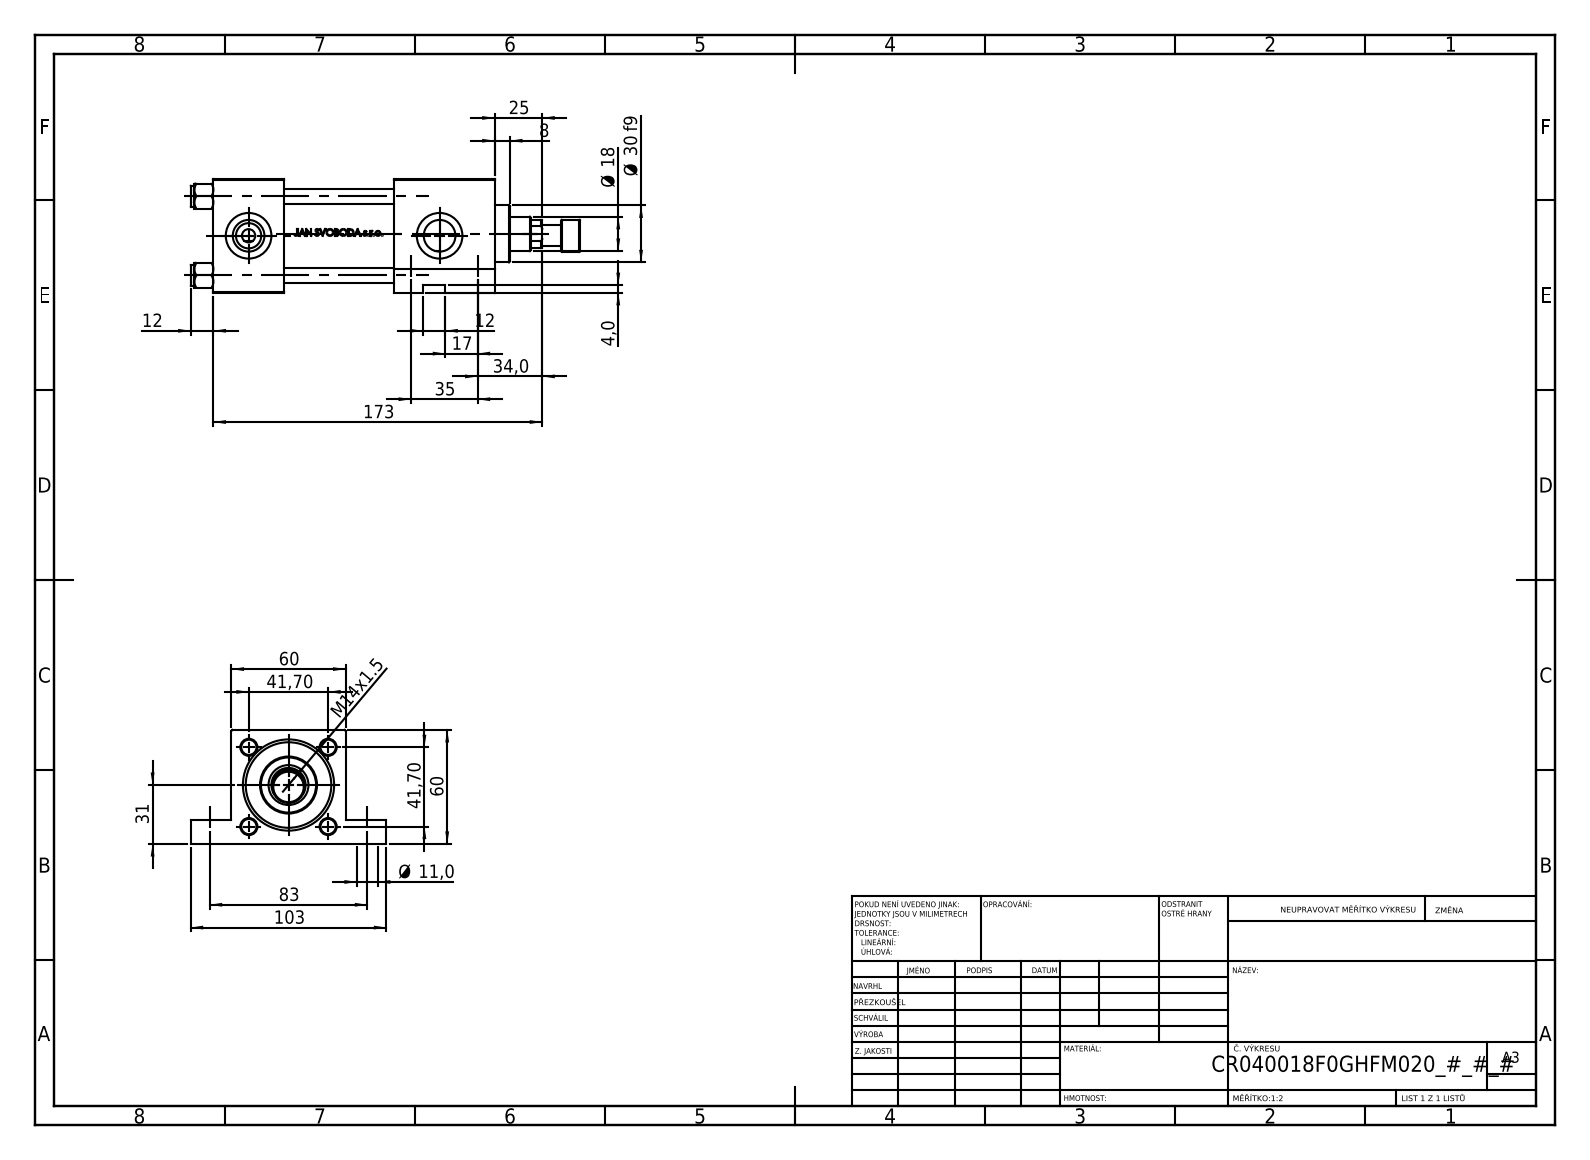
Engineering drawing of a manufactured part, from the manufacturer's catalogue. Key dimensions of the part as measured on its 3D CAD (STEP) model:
Part name (STEP PRODUCT): V215CR_F_Body; V215CR_ROD_END_F; V215CR_F_TYCINKA; V215_VC_A (+2 more)
STEP written by: SolidWorks 2019 (CONFIG_CONTROL_DESIGN)
Units: millimetres
Bodies: 12 solids, 1129 faces (440 planar, 145 cylindrical, 544 other)
Overall size (bounding box): 205 × 103 × 60
Volume: 426 846 mm³ · Surface area: 112 847 mm²
Round holes (diameter × count): ⌀8 ×4, ⌀7 ×2, ⌀11 ×2, ⌀11 ×2, ⌀16.66 ×2, ⌀24 ×2, ⌀8.5 ×1, ⌀18 ×1, ⌀21 ×1, ⌀31 ×1, ⌀40 ×1, ⌀45 ×1
Round bosses / shafts (diameter × count): ⌀11 ×5, ⌀46 ×1, ⌀30 ×1, ⌀17 ×1
Partial cylindrical surfaces — rounded edges, fillets, slot ends (radius × count): R8.5 ×1
Main face-to-face distances: 60, 37, 148, 111, 95, 58, 53, 119.3, 82.3, 24.3
Hole centre spacings: 41.7, 28.79, 30.2, 35, 58.97, 83, 90.08, 100.5
